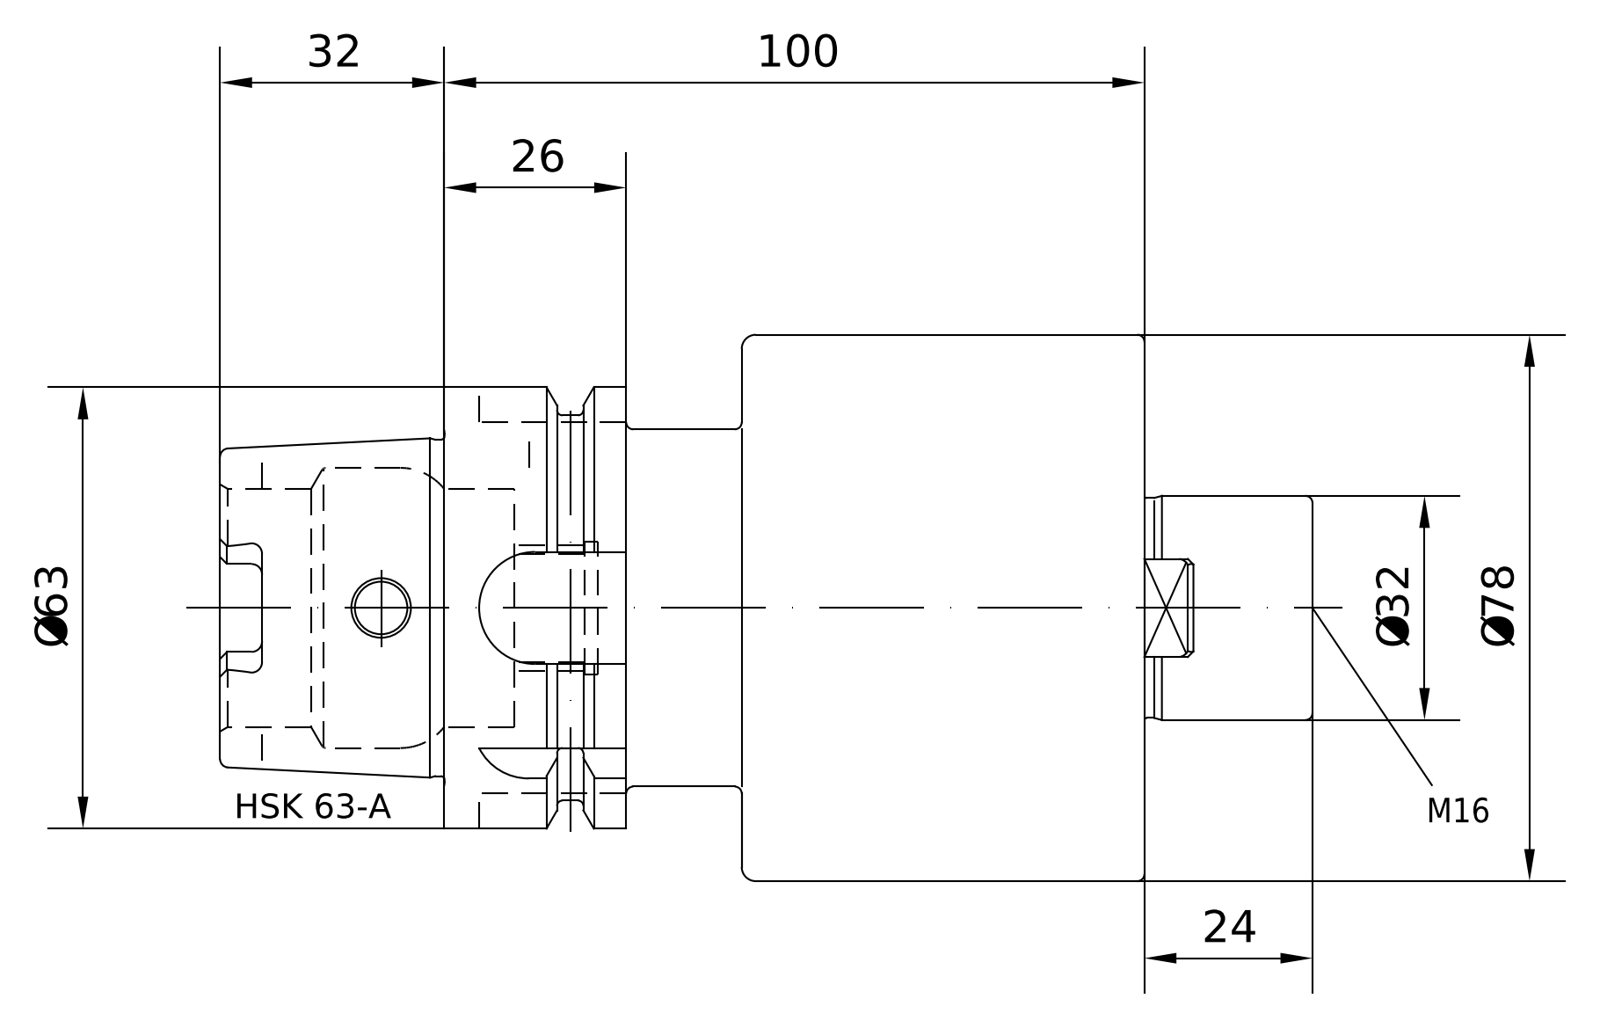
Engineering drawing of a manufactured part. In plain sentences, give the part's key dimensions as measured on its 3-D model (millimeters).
The part is named "A63-051-32". Its 3-D file was written by "PRO/ENGINEER BY PARAMETRIC TECHNOLOGY CORPORATION, 2010430 (CONFIG_CONTROL_DESIGN)". It is 1 solid with 198 faces: 70 planar, 54 cylindrical and 74 other. Overall it measures 156 by 78 by 78 millimeters. Its volume is 405 635 cubic millimeters and its surface area 50 816 square millimeters. Round holes: 1 of diameter 7.5, 1 of diameter 10, 1 of diameter 14, 1 of diameter 16, 1 of diameter 16.92, 1 of diameter 18.32, 1 of diameter 18.66, 1 of diameter 34, 1 of diameter 40. Round bosses or shafts: 1 of diameter 78, 1 of diameter 63, 1 of diameter 55, 1 of diameter 51, 1 of diameter 48.04, 1 of diameter 32, 1 of diameter 18. Partial cylindrical surfaces (rounded edges, fillets, slot ends): 6 of radius 1.5, 4 of radius 3, 1 of radius 8, 1 of radius 8.02, 1 of radius 9.02. The main face-to-face distances are 57.5, 42.5, 100, 26, 16.5, 74, 10, 124, 98, 81.5.
